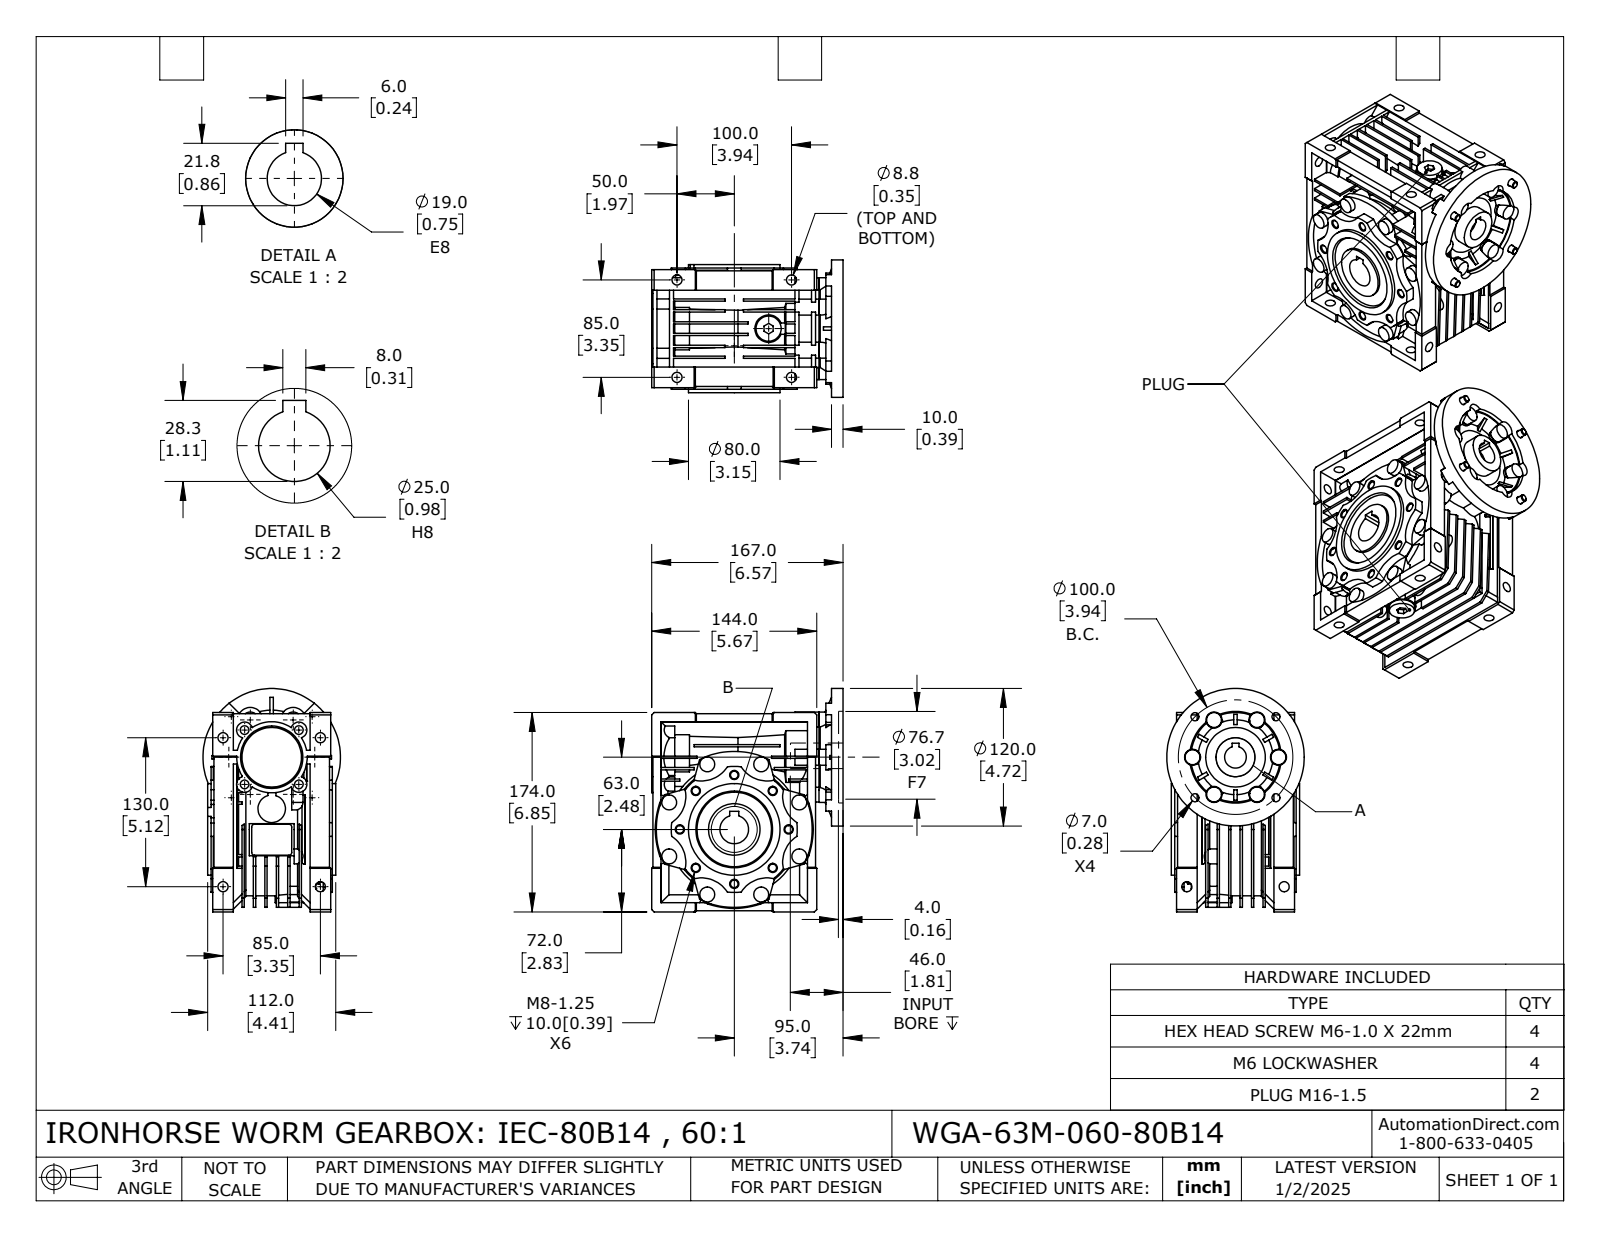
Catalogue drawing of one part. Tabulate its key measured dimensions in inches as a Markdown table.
| quantity | value |
| --- | --- |
| part name | WGA-63M-060-80B14 |
| STEP written by | SolidWorks 2024 (CONFIG_CONTROL_DESIGN) |
| units | inches |
| bodies | 16 solids, 1442 faces (853 planar, 413 cylindrical, 176 other) |
| overall size | 7.677 × 6.791 × 4.724 |
| volume | 112.7 in³ |
| surface area | 542.9 in² |
| round holes (diameter × count) | 0.262 × 8, 0.346 × 8, 0.24 × 4, 0.276 × 4, 0.298 × 4, 0.571 × 2, 0.748 × 1, 0.787 × 1, 0.984 × 1, 1.339 × 1, 1.457 × 1, 1.772 × 1 |
| round bosses / shafts (diameter × count) | 0.512 × 14, 0.551 × 6, 0.48 × 4, 0.236 × 4, 0.945 × 3, 0.866 × 2, 0.622 × 2, 0.539 × 2 |
| partial cylindrical surfaces (radius × count) | 0.276 × 10, 1.063 × 8, 0.275 × 6, 0.433 × 6, 0.098 × 4, 0.329 × 1, 1.161 × 1, 1.201 × 1 |
| main face-to-face distances | 0.394, 0.315, 0.787, 0.079, 1.181, 0.709, 0.472, 0.276, 1.575, 0.039 |
| hole center spacings | 1.431, 1.87, 2.37, 2.645, 3.456, 0.65, 1.319, 1.865 |
